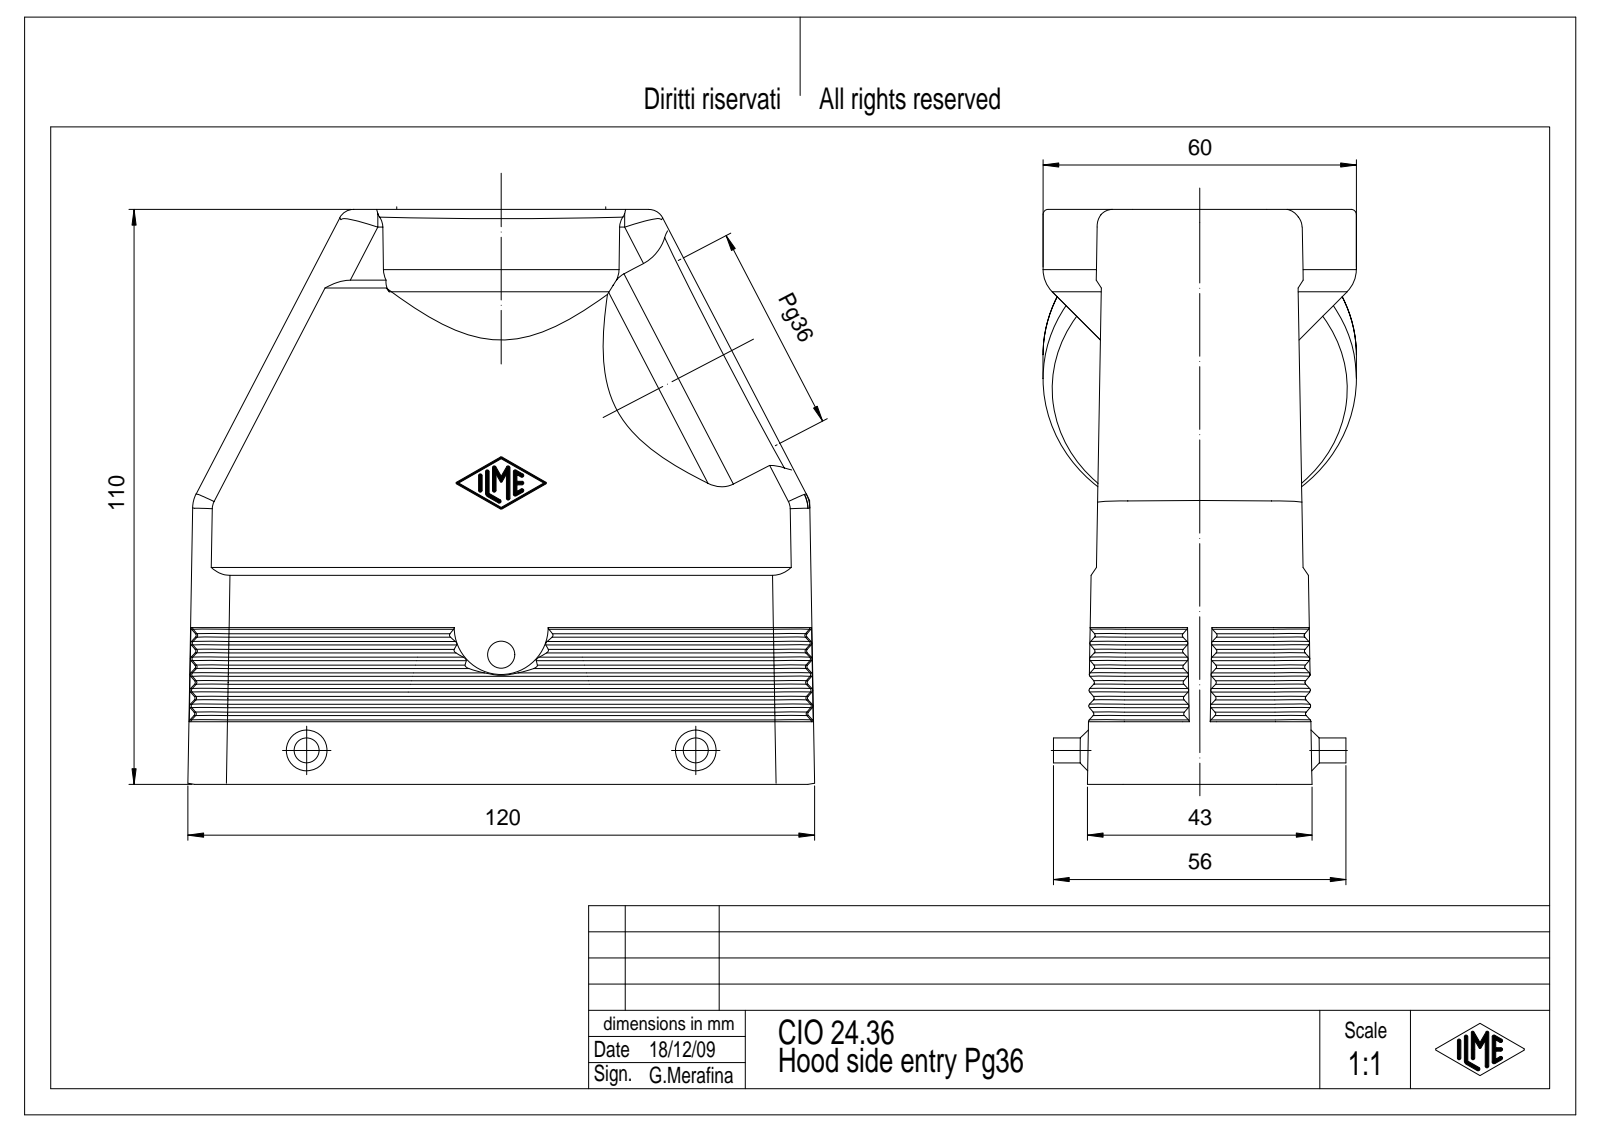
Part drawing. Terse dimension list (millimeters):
name: CIO_24.36
written by: CoCreate Modeling 16.00A 16-Aug-2008 (C) Parametric Technology GmbH (AUTOMOTIVE_DESIGN)
unit: mm
bodies: 1 solid, 572 faces (208 planar, 199 cylindrical, 165 other)
size: 119.23 × 109.2 × 60
volume: 108 233 mm³; area: 66 350 mm²
holes: 4× ⌀3.5, 1× ⌀5.2, 1× ⌀47
bosses: 2× ⌀4.8
rounds: 78× R0.5, 10× R3, 8× R7, 4× R4.2, 2× R30, 2× R33.77, 1× R1
face distances: 1.05, 2, 5.2, 2.39, 7.95, 4, 8.5, 3.99, 5.99, 7.99
hole spacings: 27, 104, 107.45
